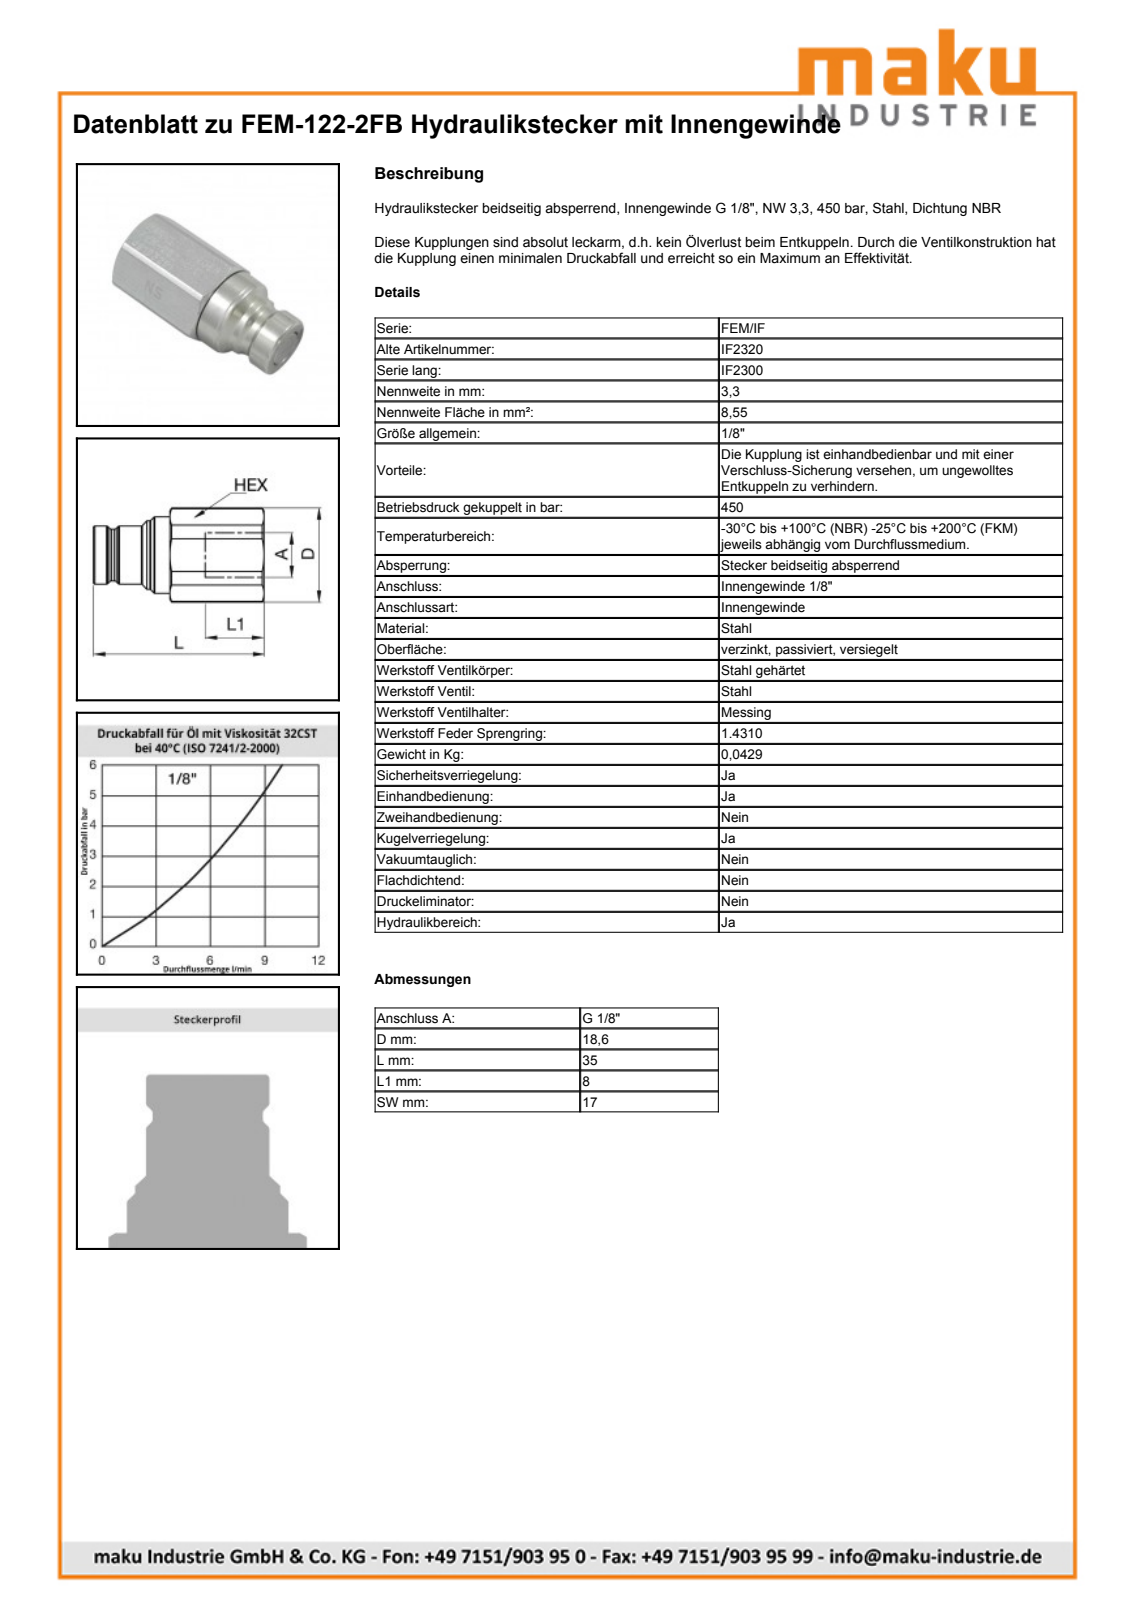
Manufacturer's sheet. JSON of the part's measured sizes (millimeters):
{"part_name": "FEM-122-2FB", "step_written_by": "SolidWorks 2009 (AUTOMOTIVE_DESIGN)", "units": "millimeters", "bodies": {"solids": 1, "faces": 60, "planar": 10, "cylindrical": 18, "other": 32}, "overall_size": [35.4, 18.6, 17], "volume_mm3": 6547, "surface_area_mm2": 2448, "round_holes": [[7.7, 1], [8.7, 1]], "round_bosses_or_shafts": [[15.8, 1], [11.65, 1], [10.15, 1]], "partial_cylinders_radius": [[9.3, 1]], "face_to_face_distances": [17, 35.4, 26.48, 8.92]}
